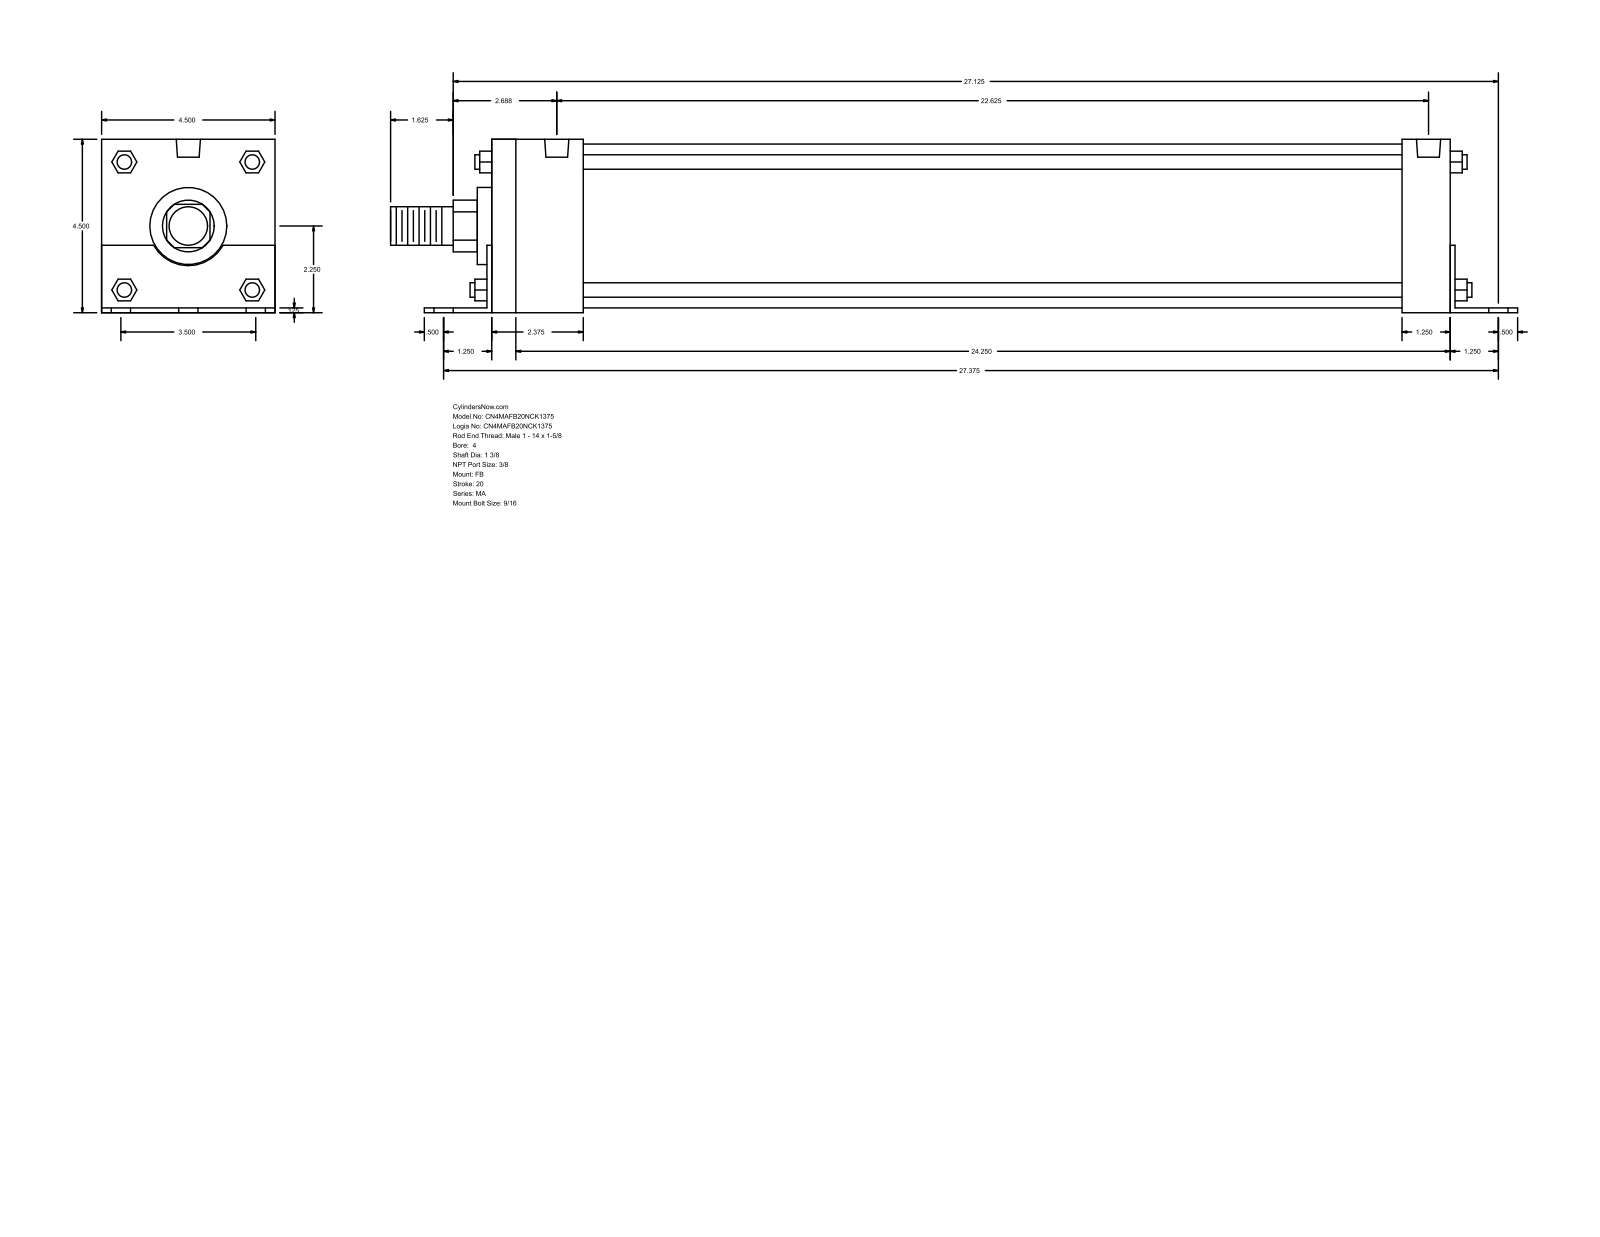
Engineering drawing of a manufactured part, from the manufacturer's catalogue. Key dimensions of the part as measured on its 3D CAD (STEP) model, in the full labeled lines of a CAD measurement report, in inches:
Part name (STEP PRODUCT): MA_FB__0400_1.375
STEP written by: GSSL Pune (CONFIG_CONTROL_DESIGN)
Units: inches
Bodies: 0 solids, 140 faces (105 planar, 35 cylindrical, 0 other)
Overall size (bounding box): 29.25 × 4.502 × 4.5
Round holes (diameter × count): ⌀0.563 ×6, ⌀0.437 ×4, ⌀0.627 ×2
Round bosses / shafts (diameter × count): ⌀0.375 ×4, ⌀4.25 ×1, ⌀2 ×1, ⌀1.375 ×1, ⌀1 ×1
Partial cylindrical surfaces — rounded edges, fillets, slot ends (radius × count): R0.672 ×1, R1.03 ×1
Main face-to-face distances: 4.5, 0.125, 4.502, 0.123, 4.377, 25, 24.875, 25.125, 1.25, 23.75
Hole centre spacings: 1.75, 27.431, 27.375, 0.188, 2.52, 2.658, 3.419, 3.5
